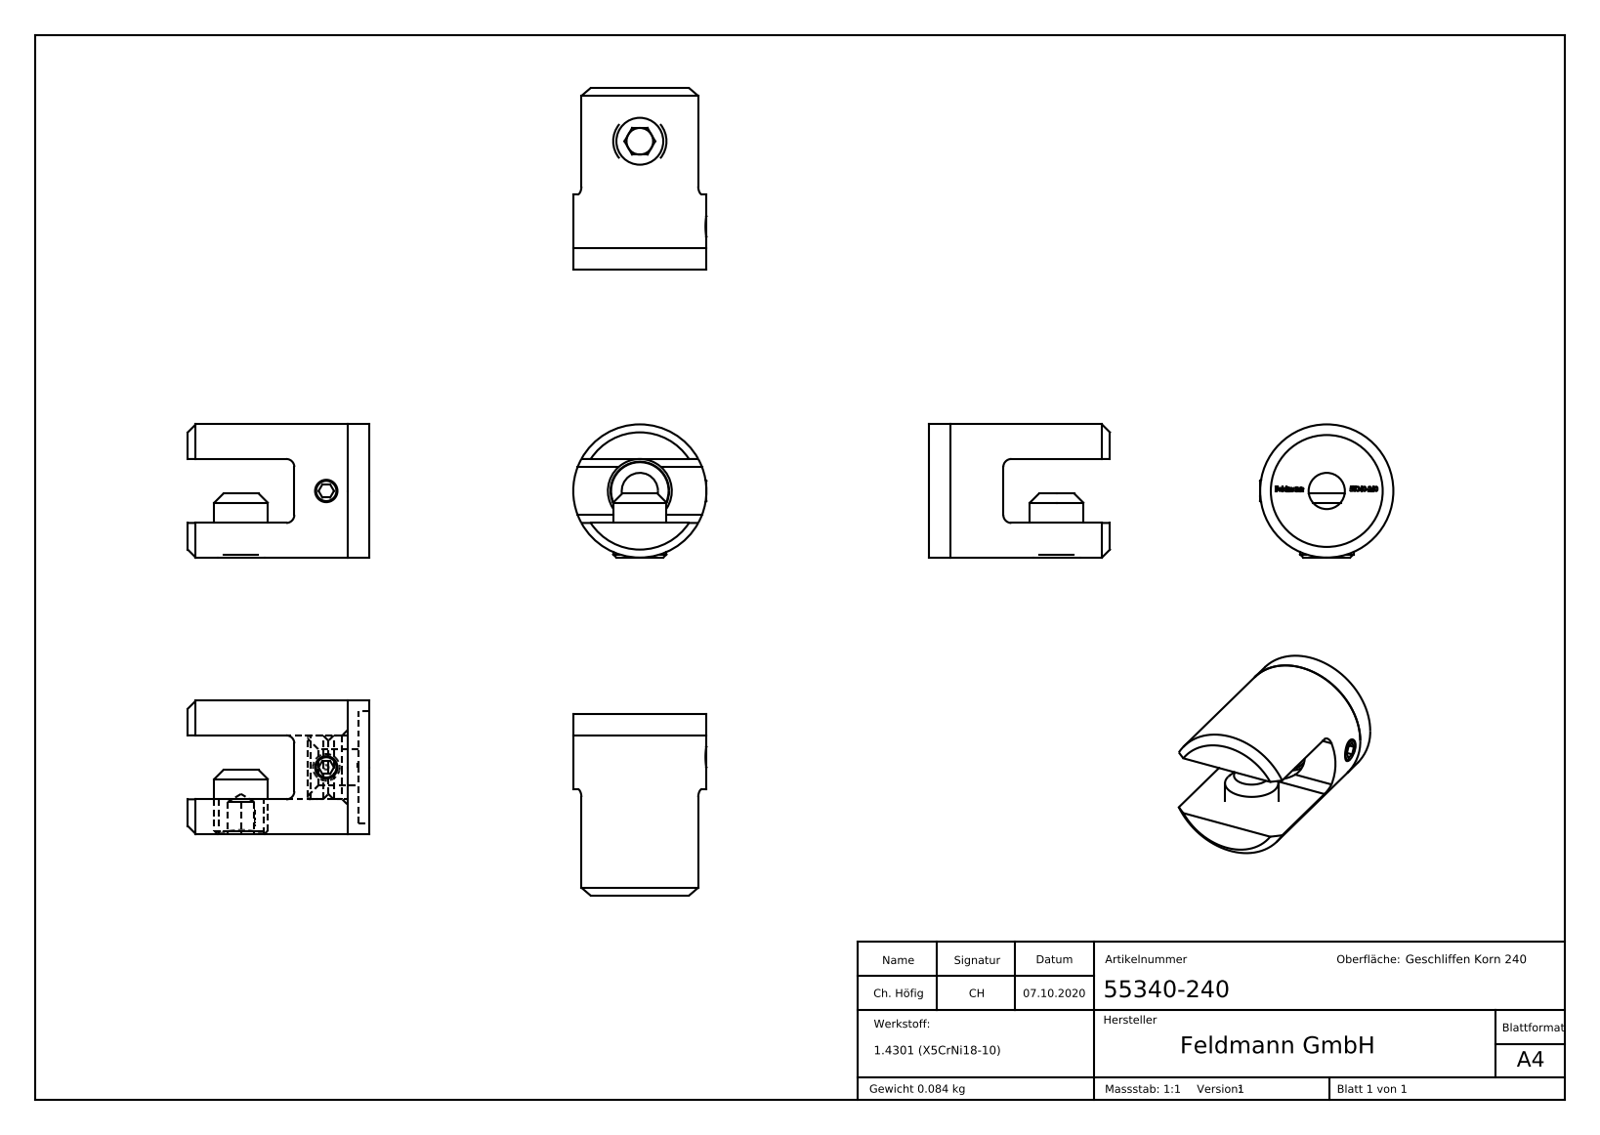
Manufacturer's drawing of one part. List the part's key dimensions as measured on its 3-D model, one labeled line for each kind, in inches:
Part name (STEP PRODUCT): 5534X-240 Teil2; 5534X-240 Teil1; DIN913_DIN 913 M10x12; DIN914 (+5 more)
STEP written by: SolidWorks 2018 (CONFIG_CONTROL_DESIGN)
Units: inches
Bodies: 4 solids, 580 faces (311 planar, 26 cylindrical, 243 other)
Overall size (bounding box): 2.756 × 2.756 × 1.339
Volume: 0.601 in³ · Surface area: 9.99 in²
Round holes (diameter × count): ⌀0.165 ×1, ⌀0.268 ×1, ⌀0.335 ×1, ⌀0.827 ×1
Round bosses / shafts (diameter × count): ⌀0.984 ×1, ⌀0.472 ×1, ⌀0.394 ×1, ⌀0.197 ×1
Partial cylindrical surfaces — rounded edges, fillets, slot ends (radius × count): R0.059 ×2
Main face-to-face distances: 0.472, 0.079, 0.157, 1.339, 1.26, 1.181, 0.394, 0.551, 0.787, 0.256
